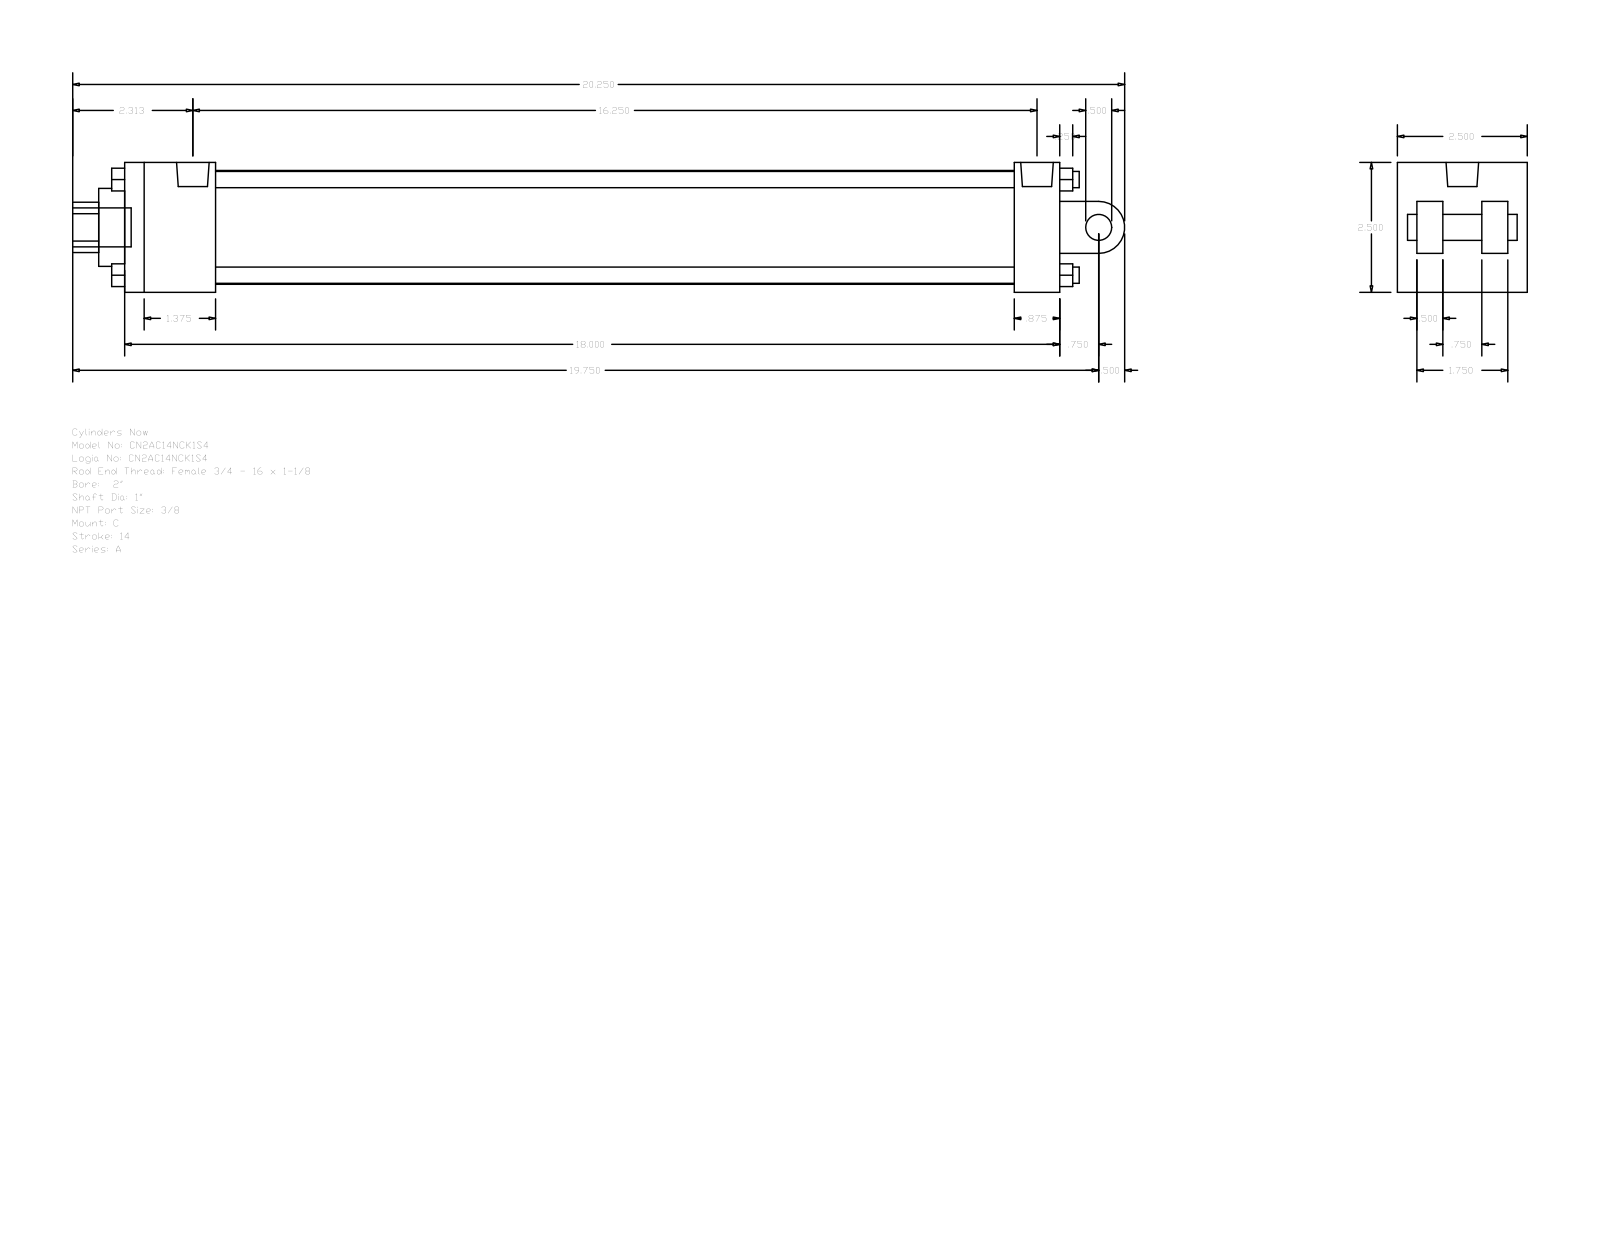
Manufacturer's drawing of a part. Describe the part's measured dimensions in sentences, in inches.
The part is named "A_C__0200_1". Its 3-D file was written by "GSSL Pune (CONFIG_CONTROL_DESIGN)". It is 0 solids with 135 faces: 102 planar, 33 cylindrical and 0 other. Overall it measures 20.25 by 2.5 by 2.5 inches. Round holes: 2 of diameter 0.219, 1 of diameter 0.627, 1 of diameter 1, 1 of diameter 1.5, 1 of diameter 2.19. Round bosses or shafts: 4 of diameter 0.313, 2 of diameter 0.219, 1 of diameter 0.75, 1 of diameter 0.627, 1 of diameter 0.5. Partial cylindrical surfaces (rounded edges, fillets, slot ends): 1 of radius 0.484, 1 of radius 0.5. The main face-to-face distances are 2.5, 0.875, 18, 1.75, 0.5, 0.375, 1.625, 16.25, 17.125, 15.375. The hole center spacings are 0.157.
